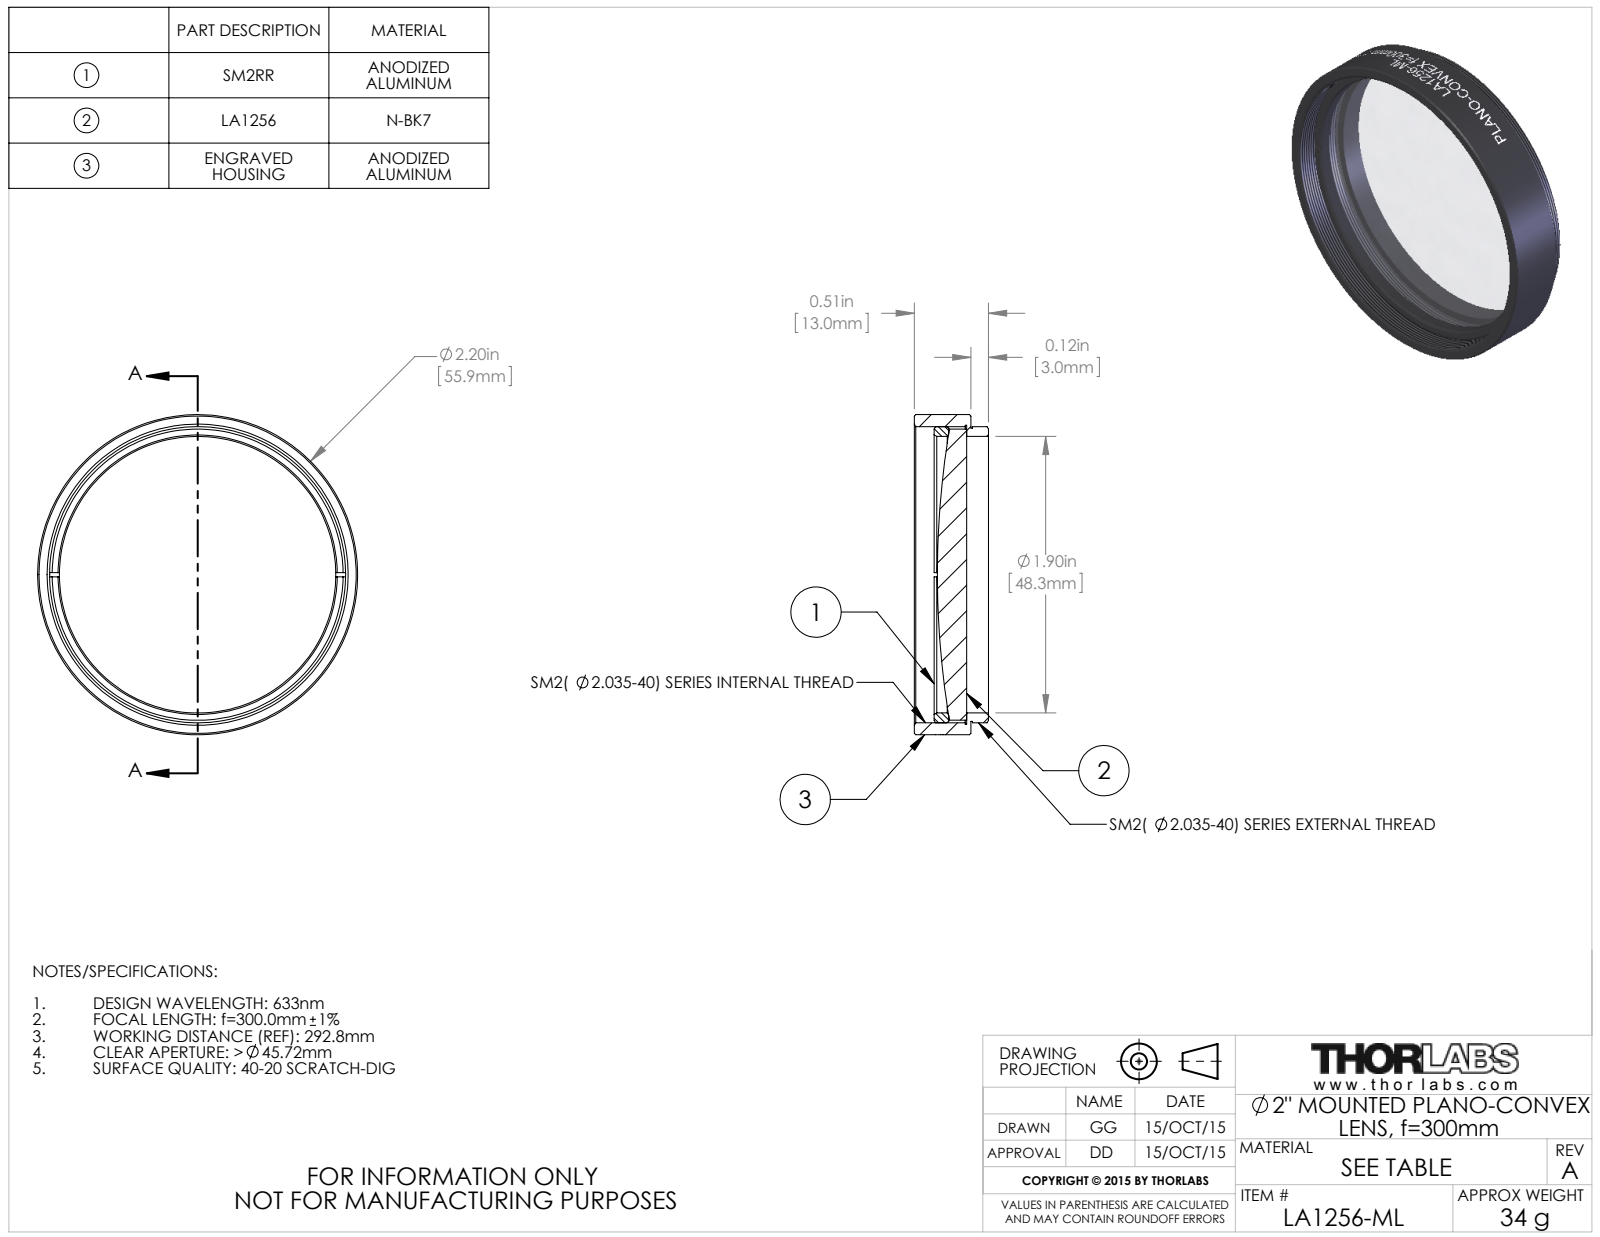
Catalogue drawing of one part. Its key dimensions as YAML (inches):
part_name: "TTN039532-E0W"
step_written_by: "SolidWorks 2014 (CONFIG_CONTROL_DESIGN)"
units: inches
bodies: {solids: 3, faces: 108, planar: 16, cylindrical: 72, other: 20}
overall_size: [2.2, 2.2, 0.51]
volume: 0.814
surface_area: 17.61
round_holes:
  - {diameter: 1.9, count: 1}
  - {diameter: 2.055, count: 1}
round_bosses_or_shafts:
  - {diameter: 2.2, count: 1}
  - {diameter: 2.035, count: 1}
  - {diameter: 2.015, count: 1}
  - {diameter: 2, count: 1}
face_to_face_distances: [0.03, 0.39, 0.36, 0.12, 0.15, 0.51, 0.274, 0.154, 0.124, 0.237]
